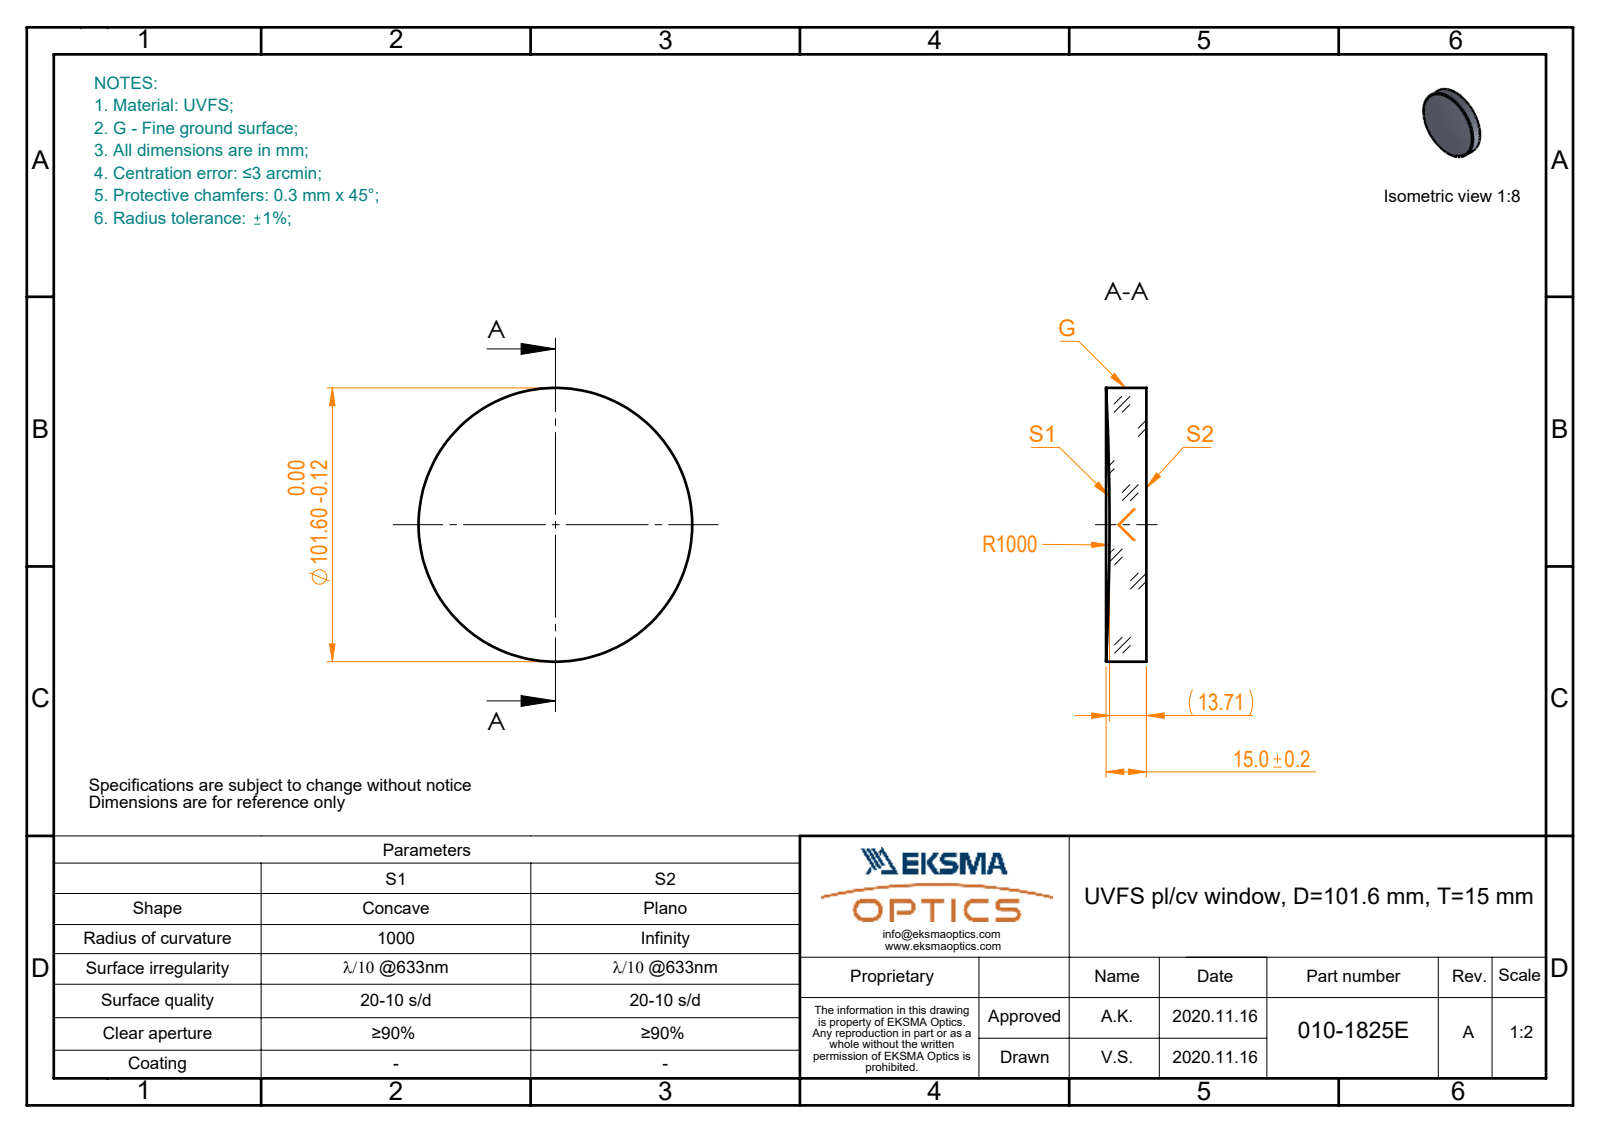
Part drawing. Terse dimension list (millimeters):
name: 010-1825E_UVFS_PCV_window
written by: SolidWorks 2019 (CONFIG_CONTROL_DESIGN)
unit: mm
bodies: 1 solid, 5 faces (1 planar, 2 cylindrical, 2 other)
size: 101.6 × 101.6 × 15
volume: 116 375 mm³; area: 21 008 mm²
bosses: 1× ⌀101.6
